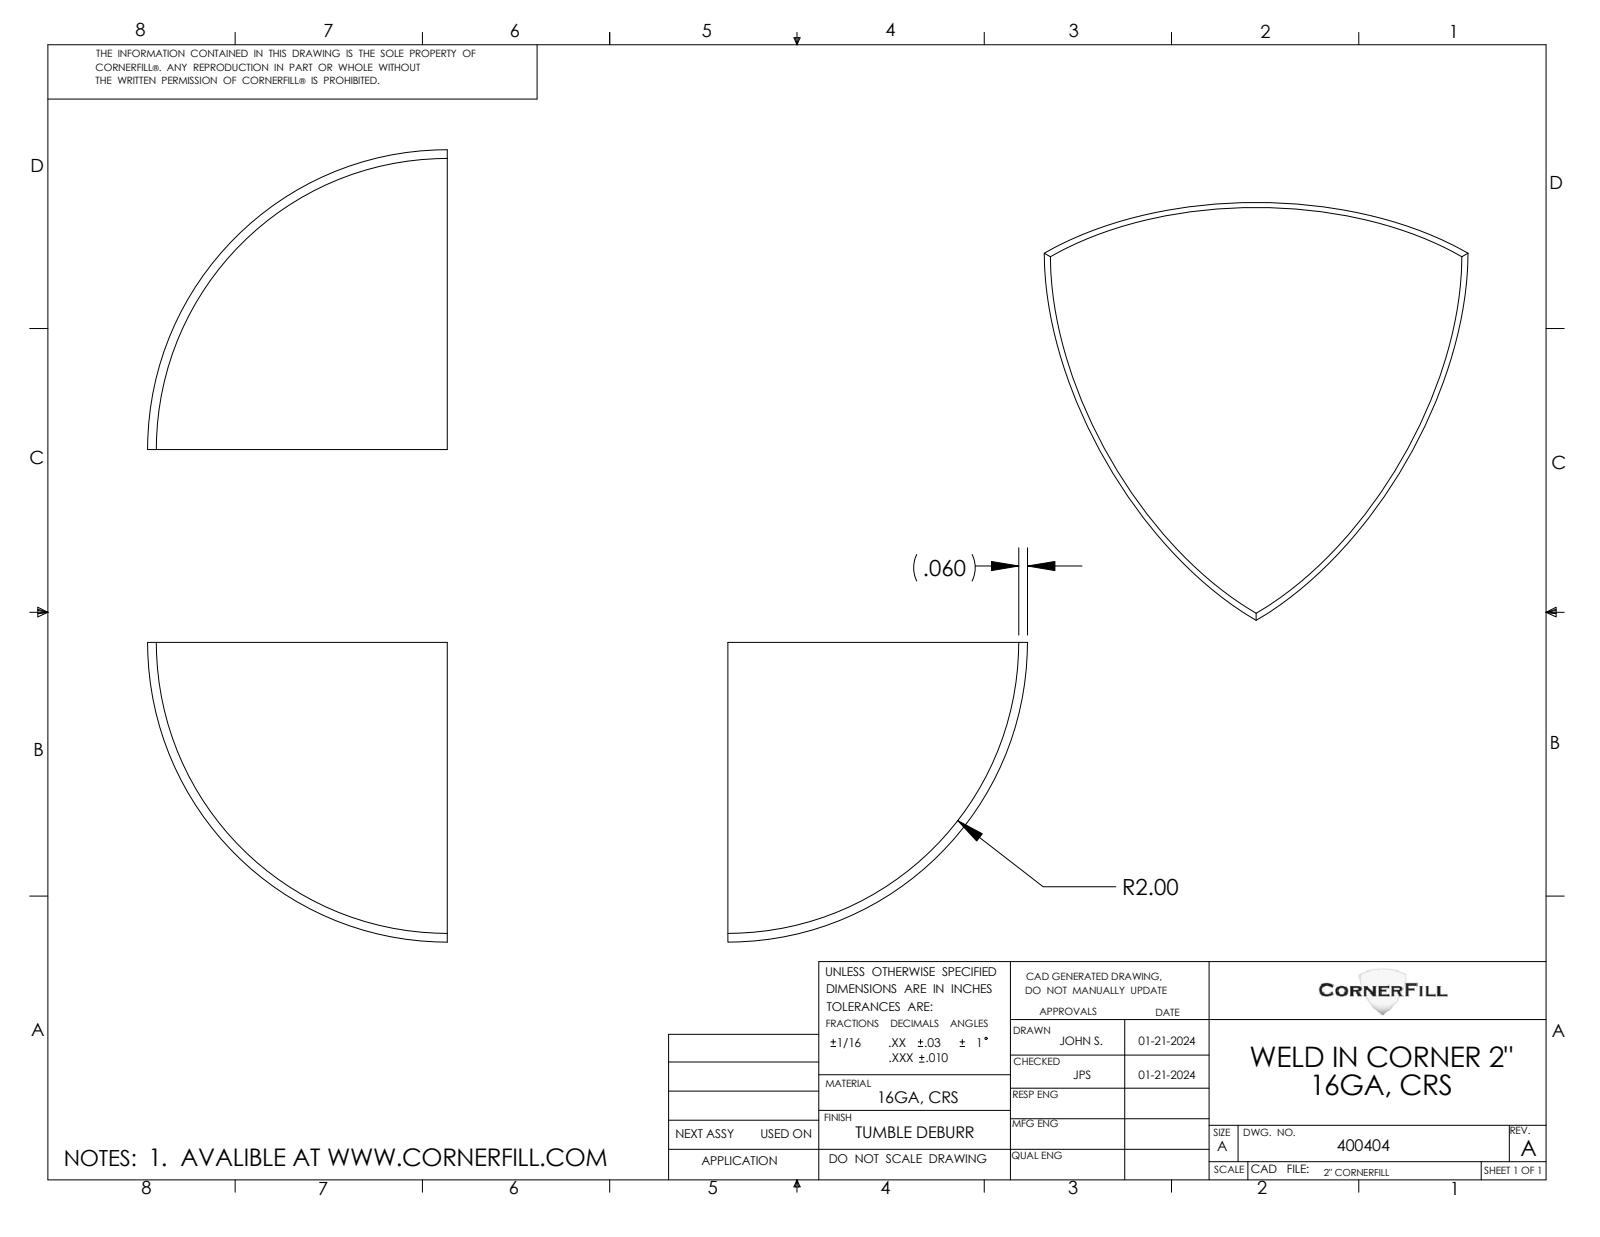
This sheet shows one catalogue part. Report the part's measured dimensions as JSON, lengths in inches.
{"part_name": "400404", "step_written_by": "SolidWorks 2021 (CONFIG_CONTROL_DESIGN)", "units": "inches", "bodies": {"solids": 1, "faces": 5, "planar": 3, "cylindrical": 0, "other": 2}, "overall_size": [2.913, 2.06, 2.06], "volume_in3": 0.388, "surface_area_in2": 13.52}
